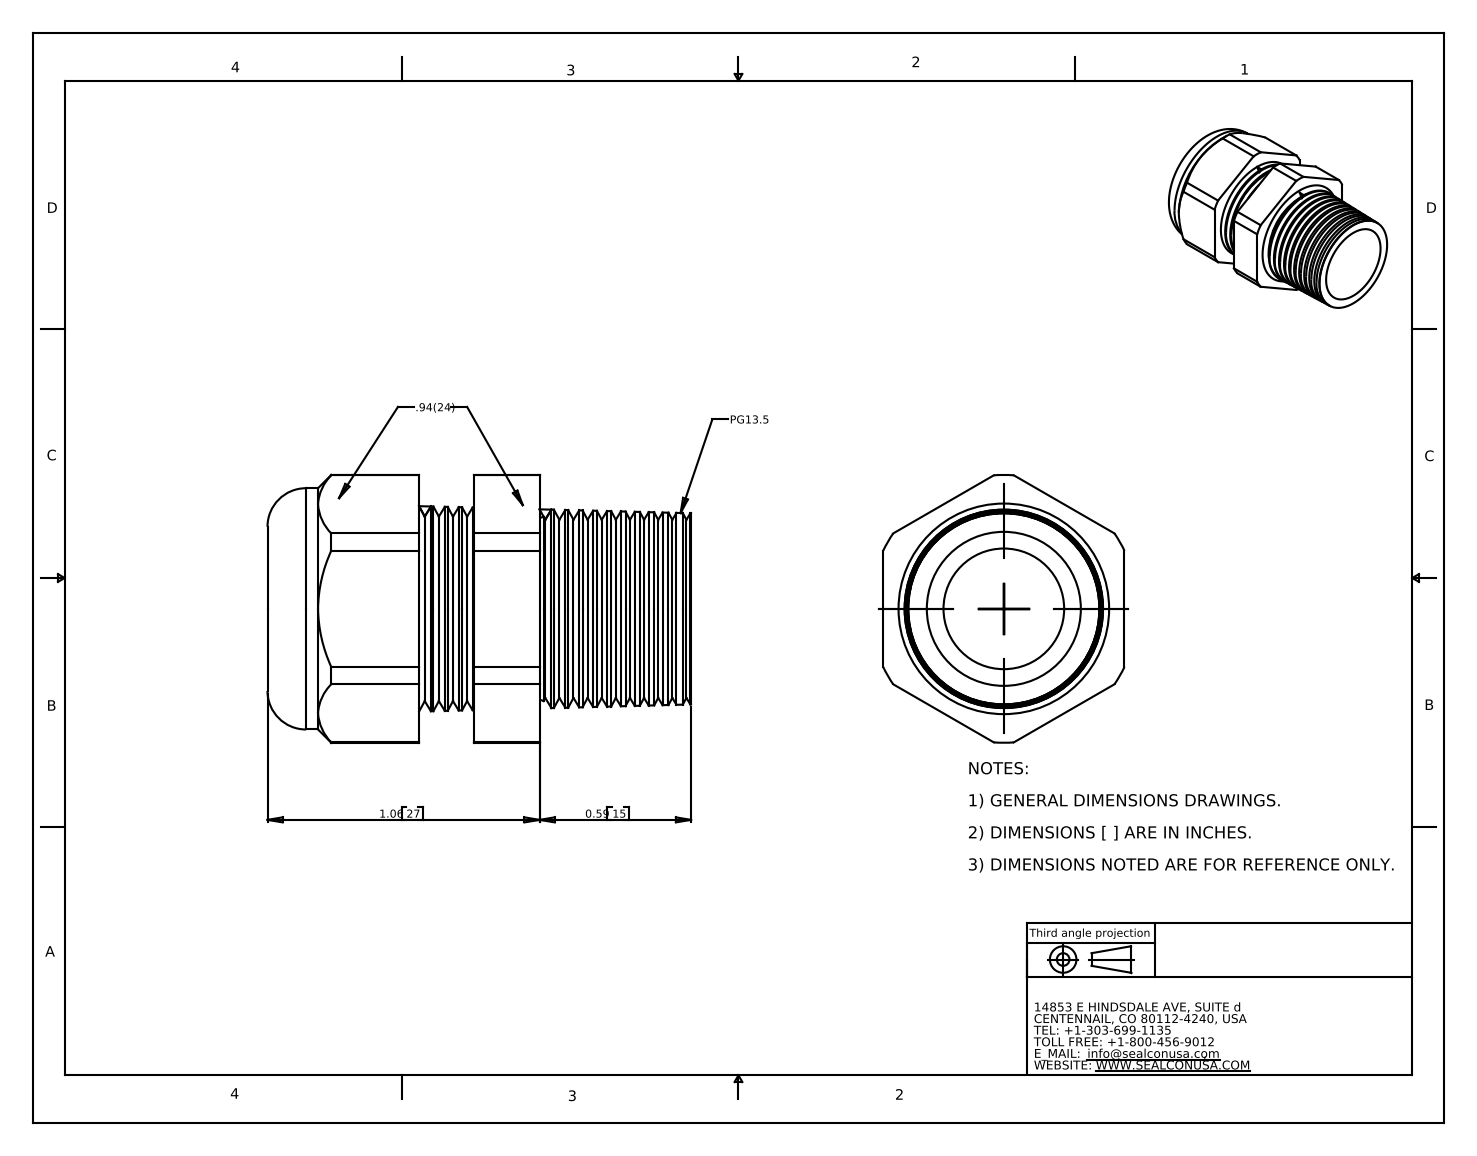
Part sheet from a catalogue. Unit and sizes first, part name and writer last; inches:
Units: inches
Overall size (bounding box): 1.65 × 1.043 × 0.94
Round holes (diameter × count): ⌀0.47 ×1, ⌀0.6 ×1
Round bosses / shafts (diameter × count): ⌀0.94 ×1
Partial cylindrical surfaces — rounded edges, fillets, slot ends (radius × count): R0.522 ×1
Main face-to-face distances: 0.94, 0.214, 0.47, 0.256, 0.394, 0.607, 0.863, 1.453, 1.059, 0.846
Volume: 0.617 in³ · Surface area: 10.82 in²
Bodies: 2 solids, 148 faces (20 planar, 22 cylindrical, 106 other)
Part name (STEP PRODUCT): CD13CA-BK
STEP written by: SolidWorks 2007 (CONFIG_CONTROL_DESIGN)
